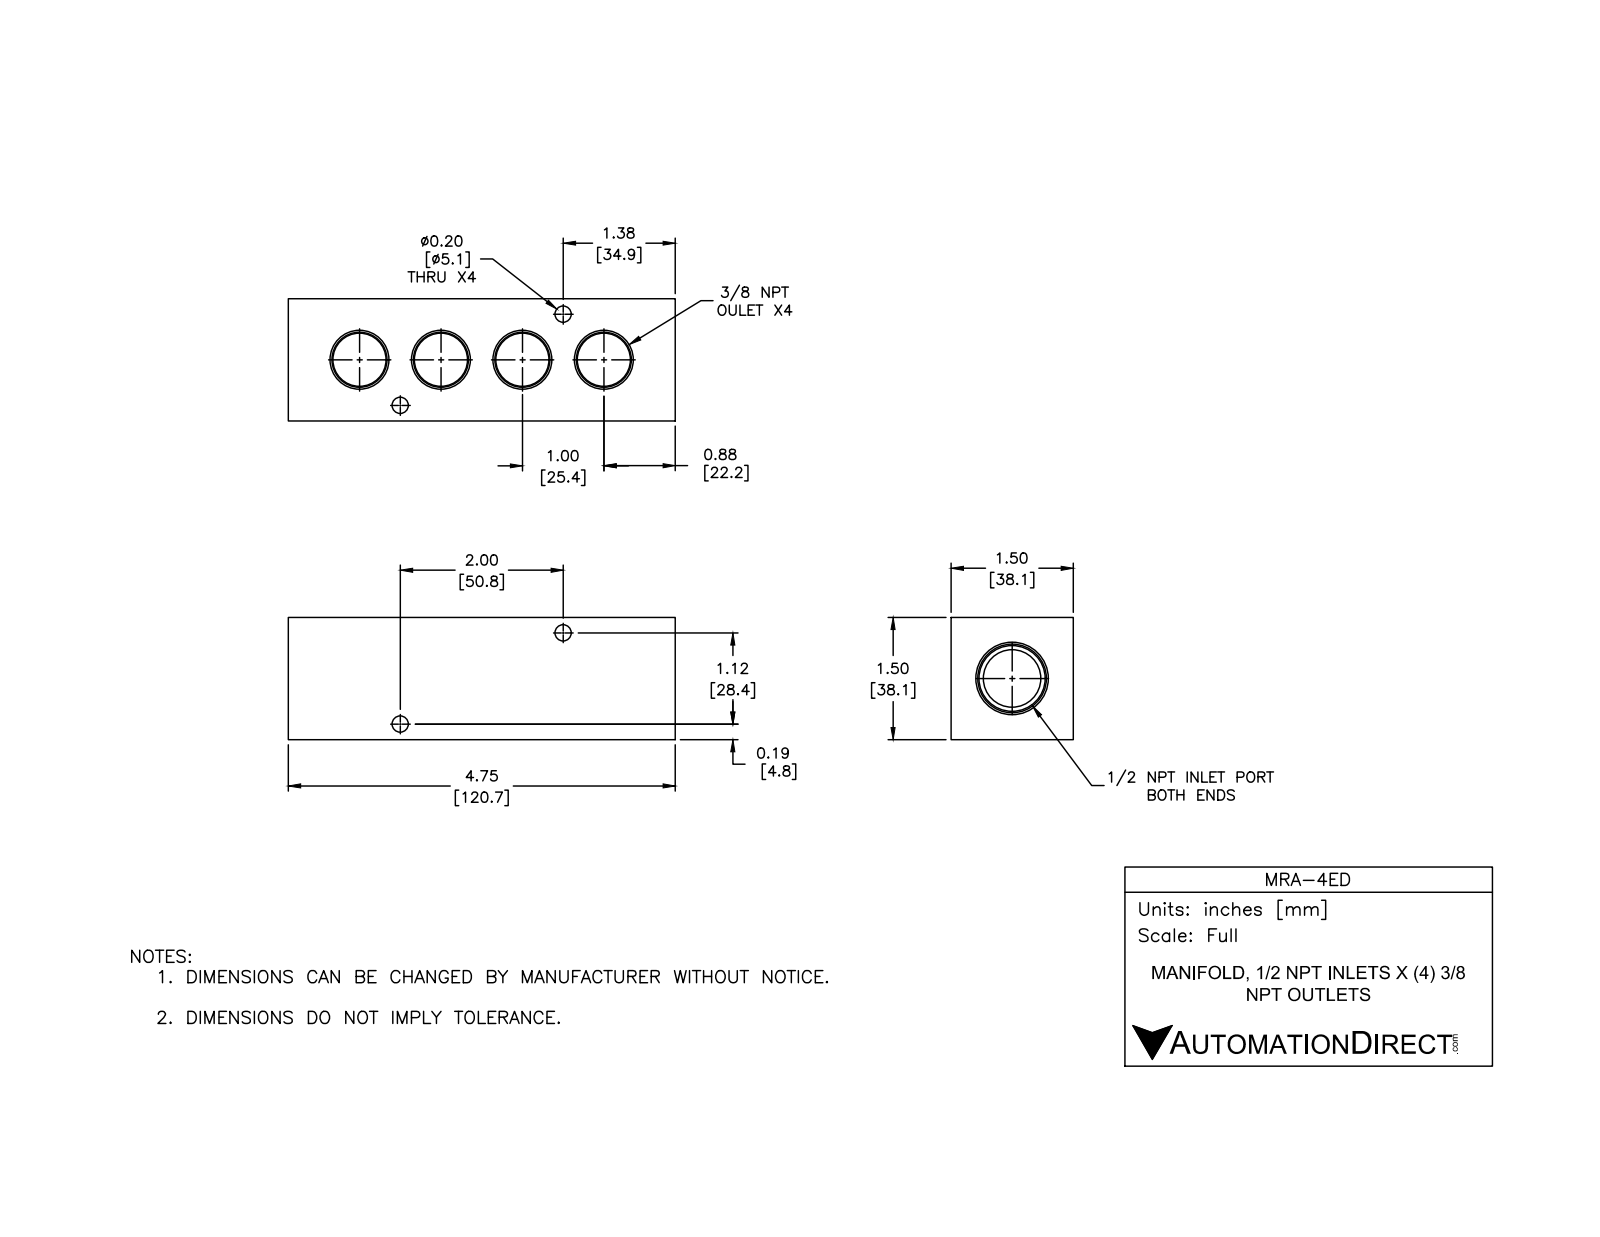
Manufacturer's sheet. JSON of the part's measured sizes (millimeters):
{"part_name": "MRA-4ED", "step_written_by": "SolidWorks 2015 (CONFIG_CONTROL_DESIGN)", "units": "millimeters", "bodies": {"solids": 1, "faces": 66, "planar": 16, "cylindrical": 26, "other": 24}, "overall_size": [120.7, 38.1, 38.1], "volume_mm3": 129800, "surface_area_mm2": 30660, "round_holes": [[5.1, 4], [14.3, 4], [17.9, 1]], "face_to_face_distances": [38.1, 120.7, 27.7, 10.4, 13.5, 107.2, 93.7], "hole_center_spacings": [19.1, 25.4, 40.7, 50.8, 58.2, 65.1, 76.2]}
